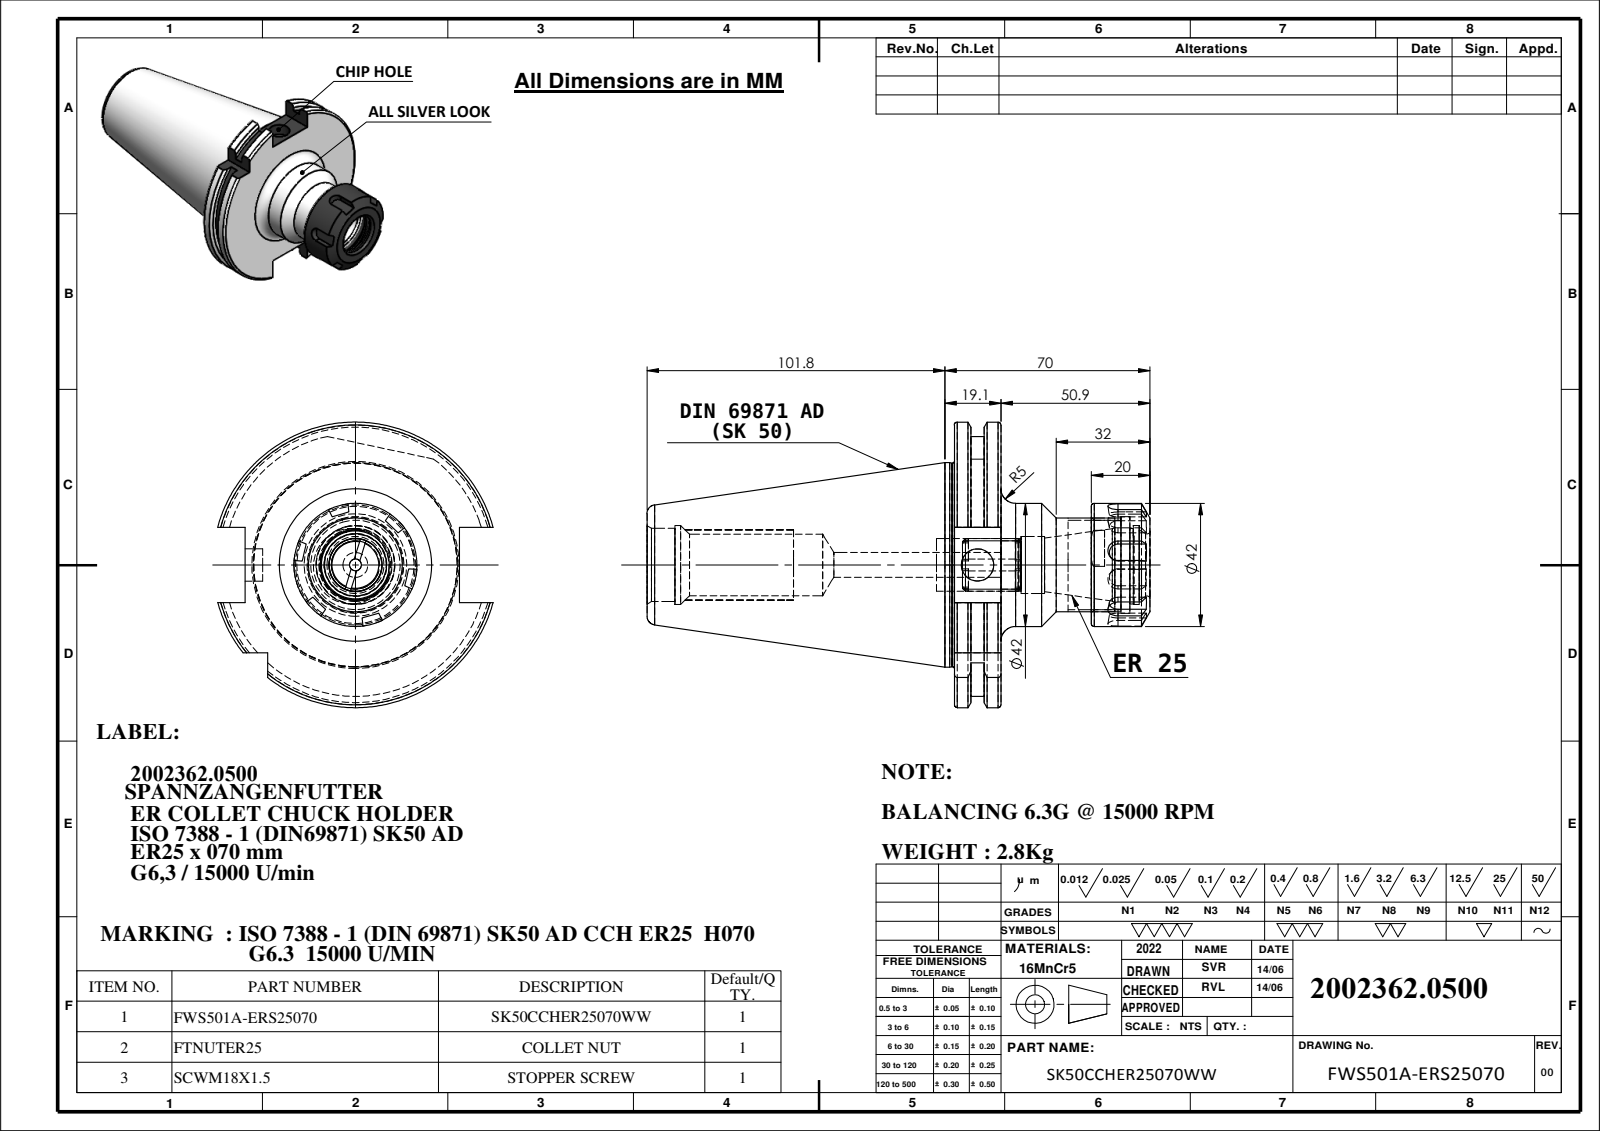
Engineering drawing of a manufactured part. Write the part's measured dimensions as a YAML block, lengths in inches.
part_name: "FTSCWM18X150; 91506-ER125070; SK50CCHER25070WW; FTNUTER25"
step_written_by: "SolidWorks 2018 (CONFIG_CONTROL_DESIGN)"
units: inches
bodies: {solids: 3, faces: 181, planar: 67, cylindrical: 49, other: 65}
overall_size: [6.762, 3.839, 3.703]
volume: 23.29
surface_area: 87.99
round_holes:
  - {diameter: 0.157, count: 1}
  - {diameter: 0.335, count: 1}
  - {diameter: 0.433, count: 1}
  - {diameter: 0.65, count: 1}
  - {diameter: 0.768, count: 1}
  - {diameter: 0.827, count: 1}
  - {diameter: 0.984, count: 1}
  - {diameter: 1.016, count: 1}
  - {diameter: 1.063, count: 1}
  - {diameter: 1.201, count: 1}
  - {diameter: 1.299, count: 1}
round_bosses_or_shafts:
  - {diameter: 2.75, count: 1}
  - {diameter: 2.734, count: 1}
  - {diameter: 1.654, count: 1}
  - {diameter: 1.26, count: 1}
  - {diameter: 0.709, count: 1}
partial_cylinders:
  - {radius: 1.768, count: 1}
  - {radius: 1.919, count: 1}
face_to_face_distances: [0.626, 1.732, 0.223, 0.403, 0.399, 0.176, 0.227, 0.787, 0.272, 0.516]
hole_center_spacings: [0.059]
